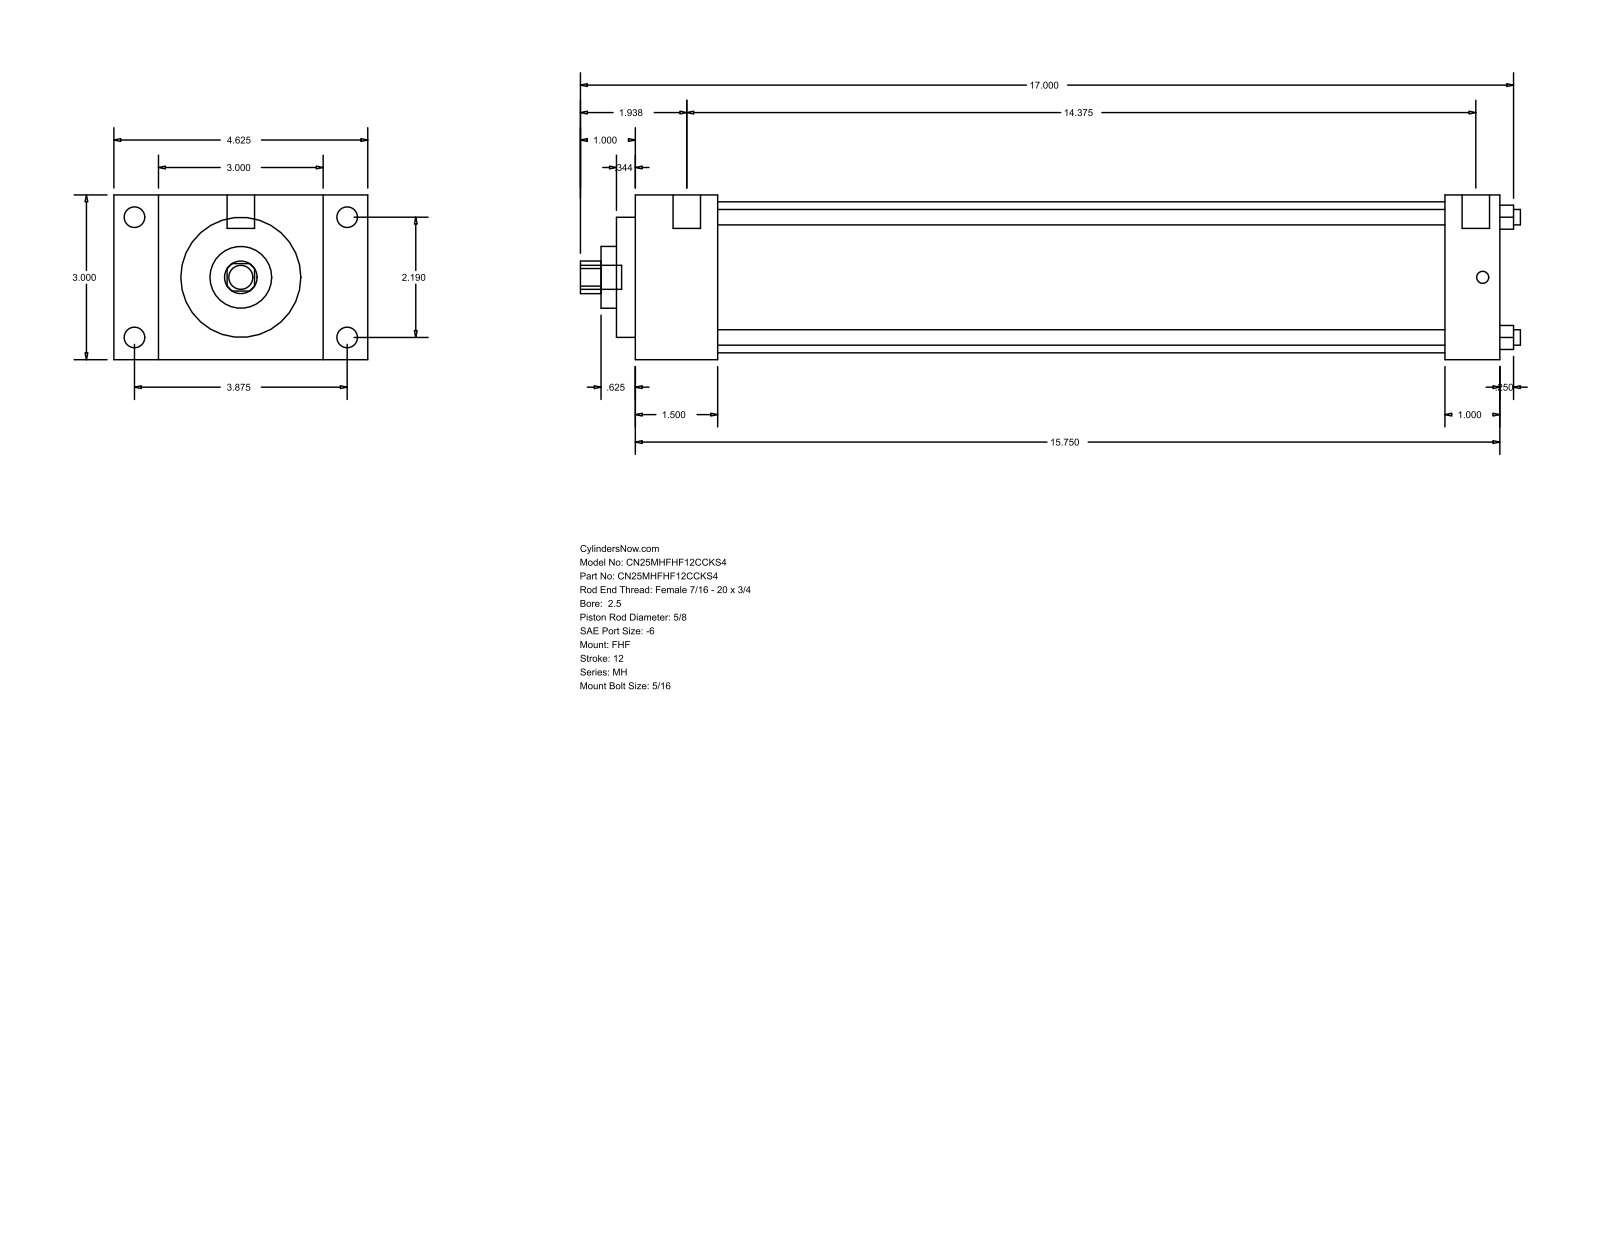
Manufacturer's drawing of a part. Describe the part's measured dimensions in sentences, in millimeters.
The part is named "MH_FHF__0250_0.625". Its 3-D file was written by "GSSL Pune (CONFIG_CONTROL_DESIGN)". It is 0 solids with 90 faces: 61 planar, 29 cylindrical and 0 other. Overall it measures 434.98 by 117.47 by 76.2 millimeters. Round holes: 4 of diameter 7.14, 1 of diameter 15.88, 1 of diameter 28.57, 1 of diameter 55.55, 1 of diameter 69.85. Round bosses or shafts: 4 of diameter 9.53, 4 of diameter 5.56, 2 of diameter 12.7, 1 of diameter 11.11. Partial cylindrical surfaces (rounded edges, fillets, slot ends): 1 of radius 7.54. The main face-to-face distances are 76.2, 400.05, 38.1, 361.95, 20.64, 96.84, 117.48, 25.4, 374.65, 336.55. The hole center spacings are 39.33, 55.62, 78.66.
